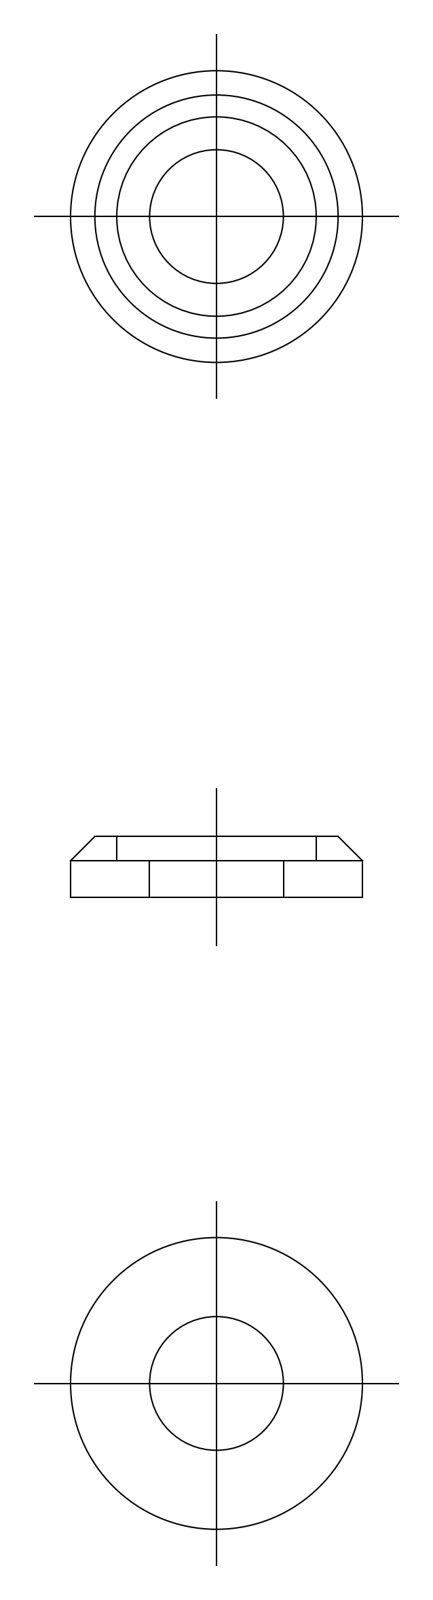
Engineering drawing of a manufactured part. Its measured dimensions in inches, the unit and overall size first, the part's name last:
Units: inches
Overall size (bounding box): 0.472 × 0.472 × 0.098
Volume: 0.011 in³ · Surface area: 0.467 in²
Bodies: 1 solid, 11 faces (0 planar, 0 cylindrical, 11 other)
Part name (STEP PRODUCT): facing ring
STEP written by: CADfix (AUTOMOTIVE_DESIGN)
